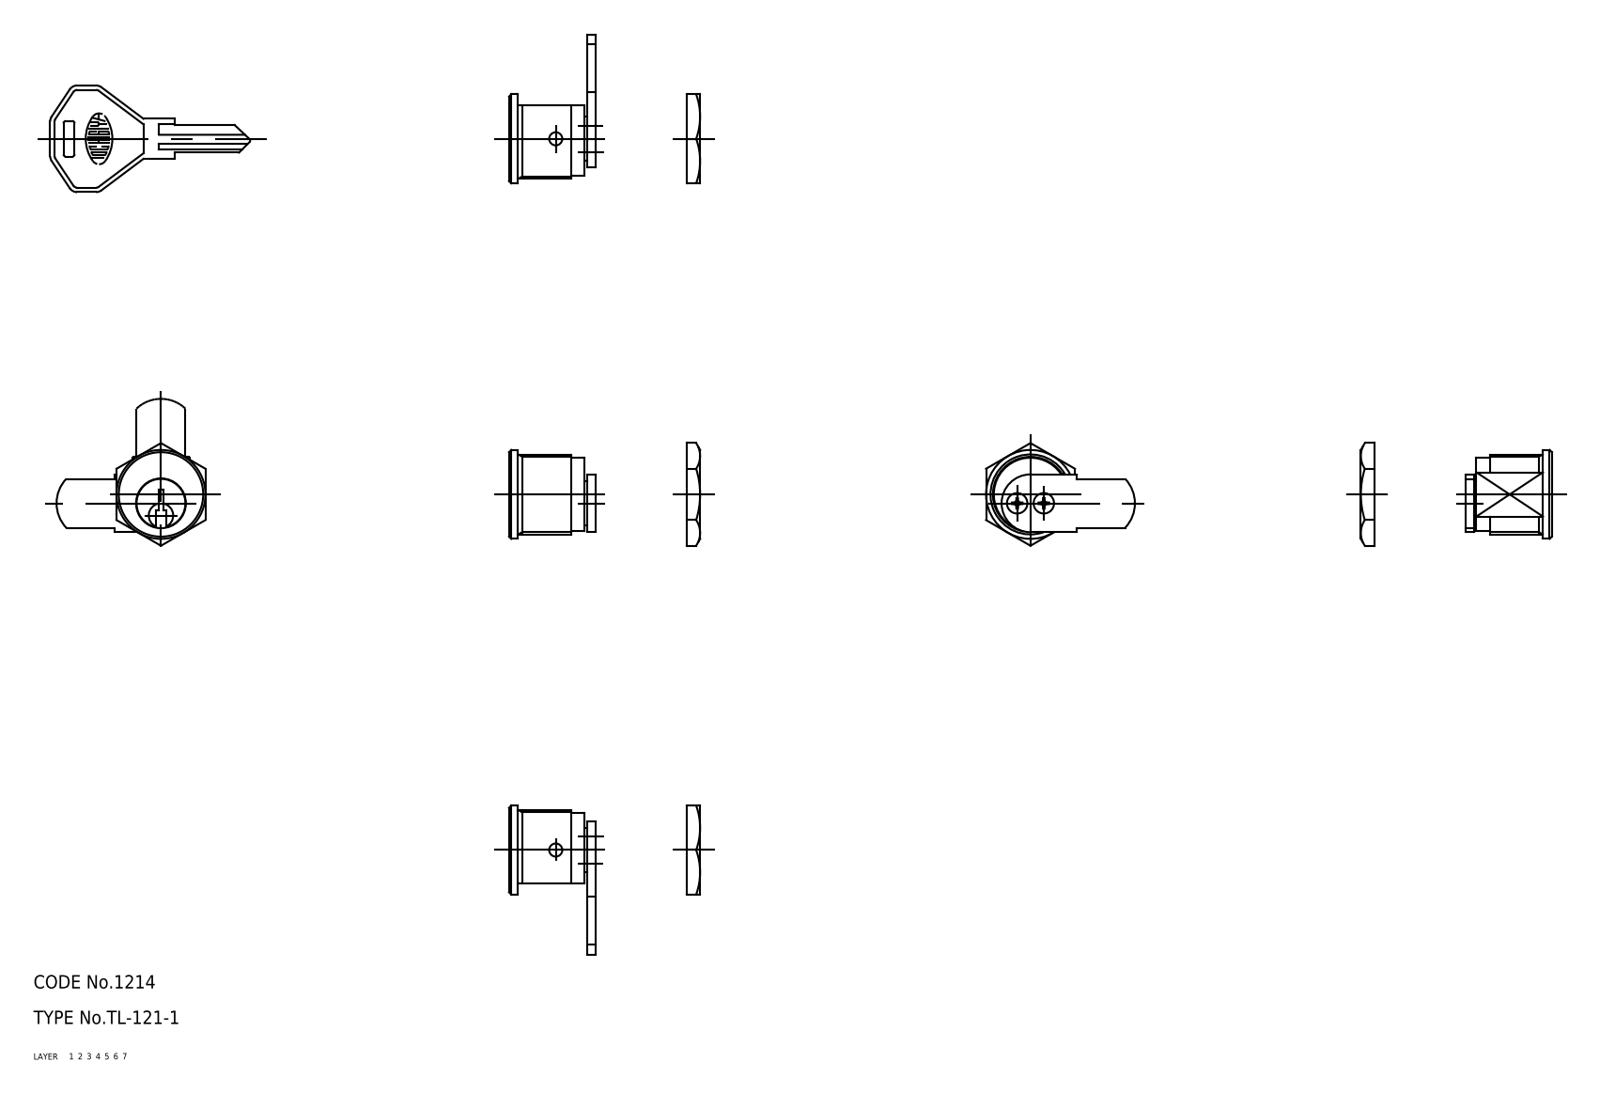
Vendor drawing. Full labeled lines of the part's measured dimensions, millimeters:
Part name (STEP PRODUCT): screw; cam; nut; lock (+2 more)
STEP written by: CADfix (AUTOMOTIVE_DESIGN)
Units: millimetres
Bodies: 6 solids, 162 faces (0 planar, 0 cylindrical, 162 other)
Overall size (bounding box): 86.44 × 33.5 × 25.95
Volume: 5 666 mm³ · Surface area: 4 849 mm²
